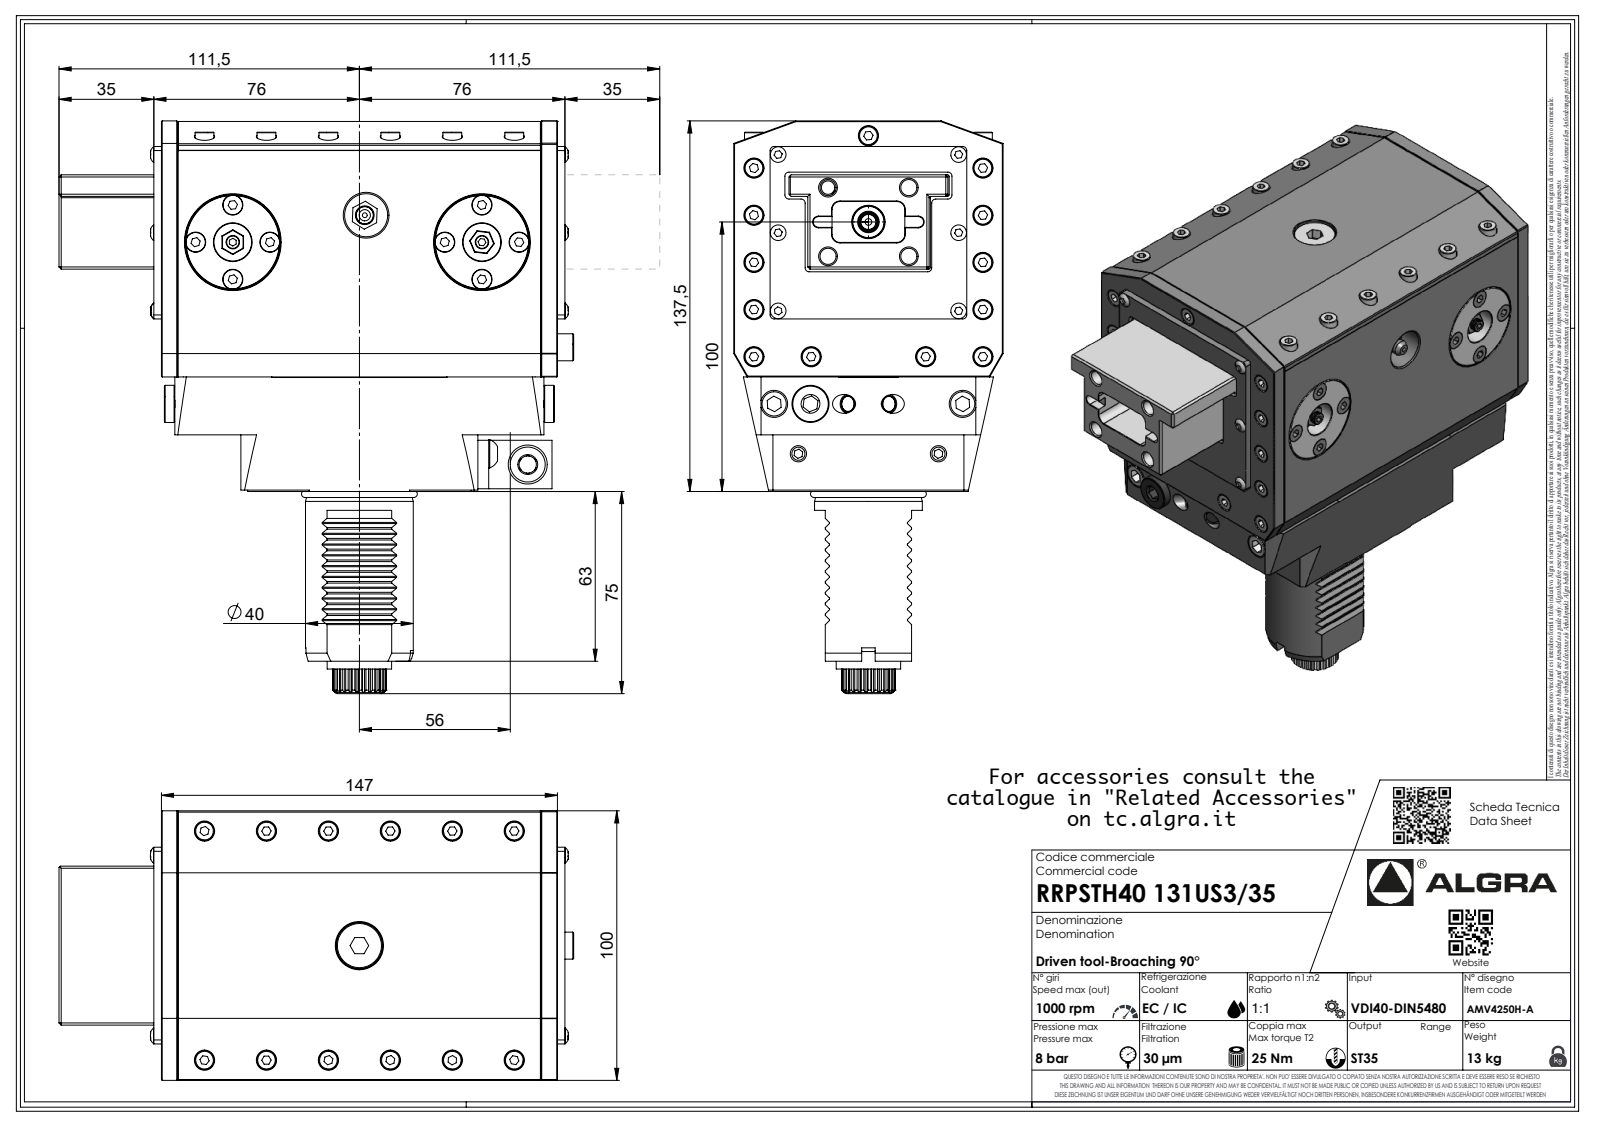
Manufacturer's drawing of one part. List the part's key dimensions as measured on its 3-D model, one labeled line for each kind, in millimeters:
Part name (STEP PRODUCT): RRPSTH40131US335
STEP written by: SolidWorks 2023 (AUTOMOTIVE_DESIGN)
Units: millimetres
Bodies: 1 solid, 1104 faces (712 planar, 167 cylindrical, 225 other)
Overall size (bounding box): 212.5 × 191.05 × 100
Volume: 1 942 000 mm³ · Surface area: 121 040 mm²
Round holes (diameter × count): ⌀2.1 ×1, ⌀10 ×1
Round bosses / shafts (diameter × count): ⌀7 ×12, ⌀3 ×4, ⌀55 ×1, ⌀40 ×1, ⌀38.7 ×1, ⌀23.9 ×1, ⌀6.37 ×1, ⌀1.7 ×1
Partial cylindrical surfaces — rounded edges, fillets, slot ends (radius × count): R0.3 ×20, R0.5 ×10, R3 ×9, R0.33 ×7, R0.52 ×7, R3.7 ×7, R1.5 ×6, R0.21 ×1
Main face-to-face distances: 100, 149.8, 2.8, 147, 116.3, 1, 21.5, 117.5, 21, 137.3
